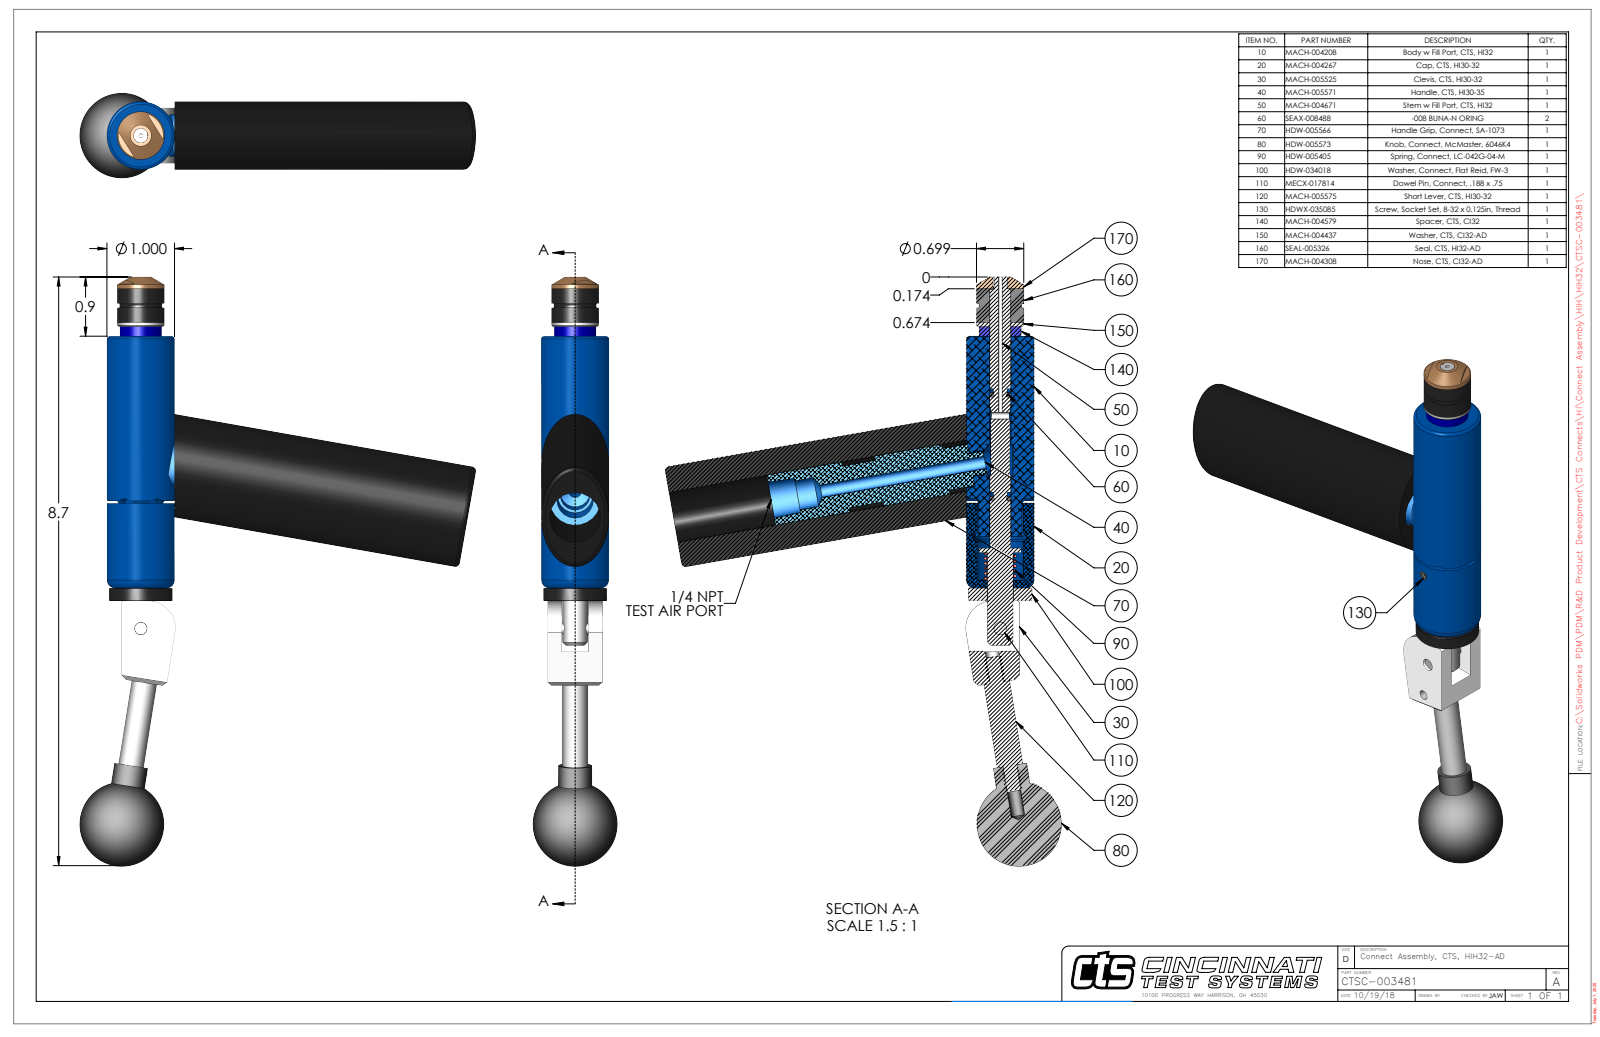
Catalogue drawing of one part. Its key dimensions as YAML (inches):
part_name: "CTSC-003481"
step_written_by: "SolidWorks 2023 (AUTOMOTIVE_DESIGN)"
units: inches
bodies: {solids: 11, faces: 308, planar: 113, cylindrical: 127, other: 68}
overall_size: [8.704, 5.856, 1.25]
volume: 9.35
surface_area: 77.85
round_holes:
  - {diameter: 0.201, count: 2}
  - {diameter: 0.063, count: 1}
  - {diameter: 0.109, count: 1}
  - {diameter: 0.136, count: 1}
  - {diameter: 0.15, count: 1}
  - {diameter: 0.187, count: 1}
  - {diameter: 0.189, count: 1}
  - {diameter: 0.213, count: 1}
  - {diameter: 0.31, count: 1}
  - {diameter: 0.314, count: 1}
  - {diameter: 0.316, count: 1}
  - {diameter: 0.385, count: 1}
round_bosses_or_shafts:
  - {diameter: 0.25, count: 2}
  - {diameter: 0.201, count: 2}
  - {diameter: 1, count: 1}
  - {diameter: 0.936, count: 1}
  - {diameter: 0.75, count: 1}
  - {diameter: 0.699, count: 1}
  - {diameter: 0.62, count: 1}
  - {diameter: 0.618, count: 1}
partial_cylinders:
  - {radius: 0.093, count: 6}
  - {radius: 0.029, count: 2}
  - {radius: 0.088, count: 1}
  - {radius: 0.325, count: 1}
  - {radius: 0.4, count: 1}
  - {radius: 0.455, count: 1}
face_to_face_distances: [0.21, 0.602, 3.719, 0.812, 3.906, 0.187, 0.702, 4.42, 4.608, 0.5]
hole_center_spacings: [0.599, 1.658, 2.252]
